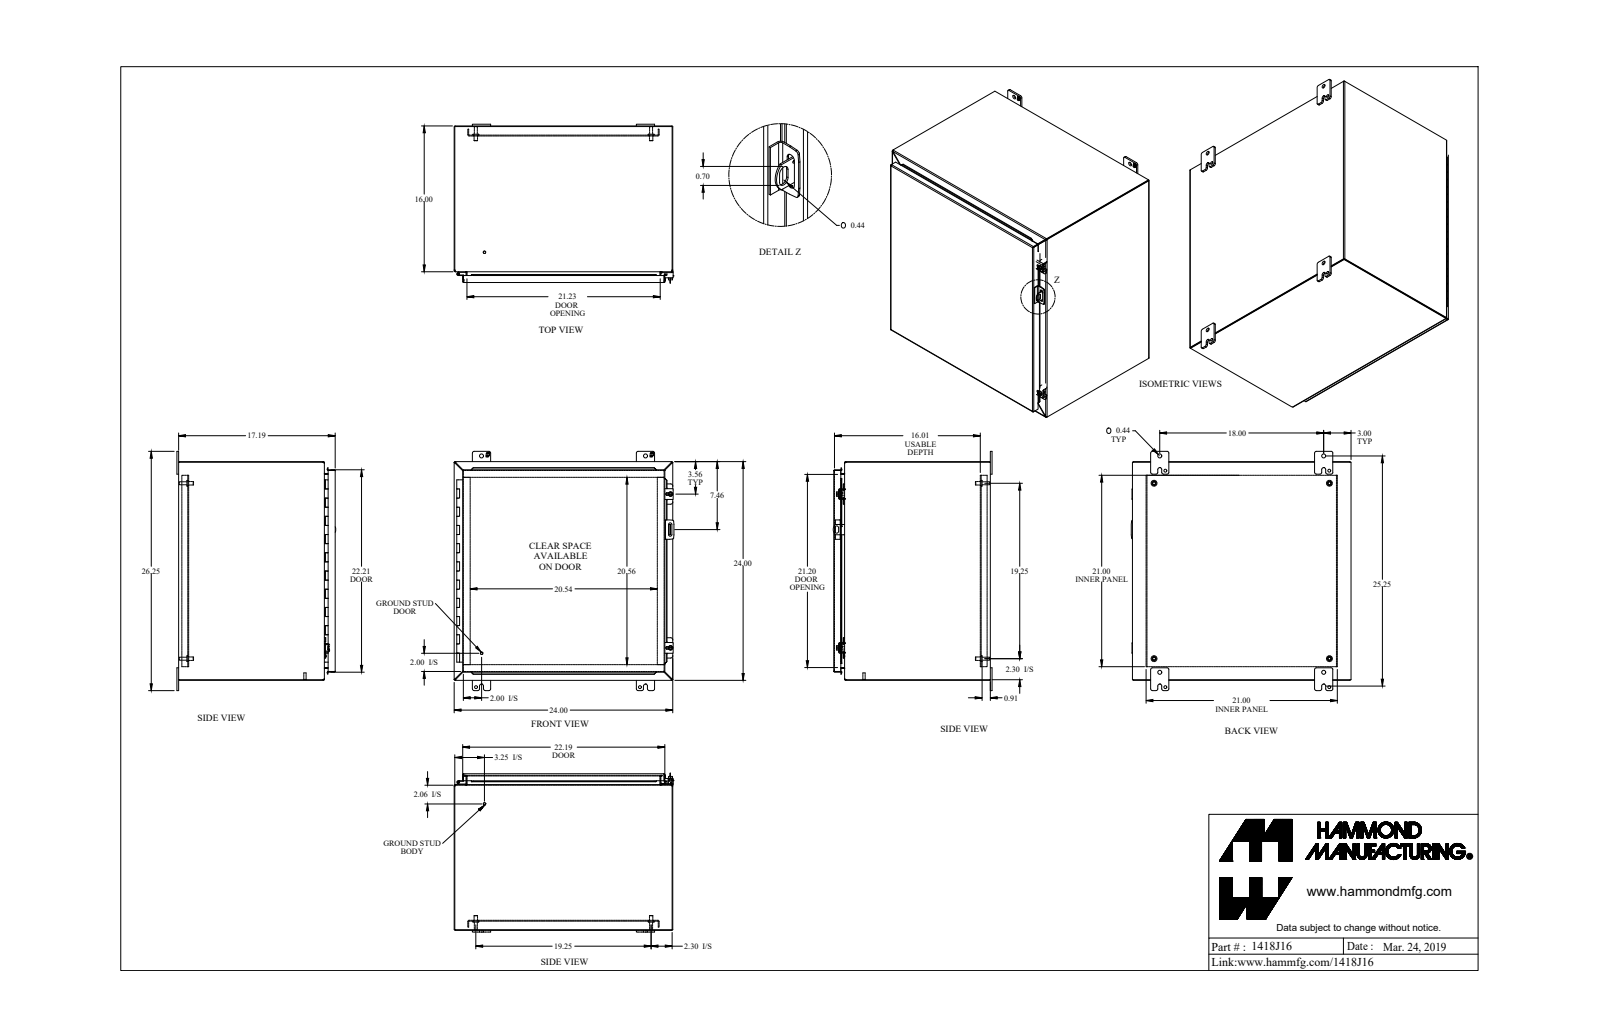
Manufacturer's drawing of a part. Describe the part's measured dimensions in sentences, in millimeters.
The part is named "1418J16". Its 3-D file was written by "SolidWorks 2019 (AUTOMOTIVE_DESIGN)". It is 40 solids with 1006 faces: 677 planar, 267 cylindrical and 62 other. Overall it measures 666.8 by 612.8 by 442.9 millimeters. Its volume is 4 477 000 cubic millimeters and its surface area 4 637 000 square millimeters. Round holes: 4 of diameter 8, 4 of diameter 11.1, 4 of diameter 12.7, 2 of diameter 5.4, 2 of diameter 6.7, 2 of diameter 7.8, 2 of diameter 9.5, 1 of diameter 3.2, 1 of diameter 4.7, 1 of diameter 11.3, 1 of diameter 11.3. Round bosses or shafts: 4 of diameter 16.5, 4 of diameter 9.5, 4 of diameter 8.4, 2 of diameter 25.4, 2 of diameter 12.7, 2 of diameter 9.9, 2 of diameter 7.1, 2 of diameter 6.4. Partial cylindrical surfaces (rounded edges, fillets, slot ends): 26 of radius 4.8, 18 of radius 0.9, 18 of radius 2.7, 13 of radius 1.2, 13 of radius 3.6, 12 of radius 6.4, 8 of radius 0.2, 8 of radius 1. The main face-to-face distances are 1.8, 607.8, 434.7, 605.9, 609.6, 432.8, 436.5, 23.8, 2.4, 25.6. The hole center spacings are 489, 457.2, 44.1, 61.8, 77.9, 527.3, 603.3, 691.5.
